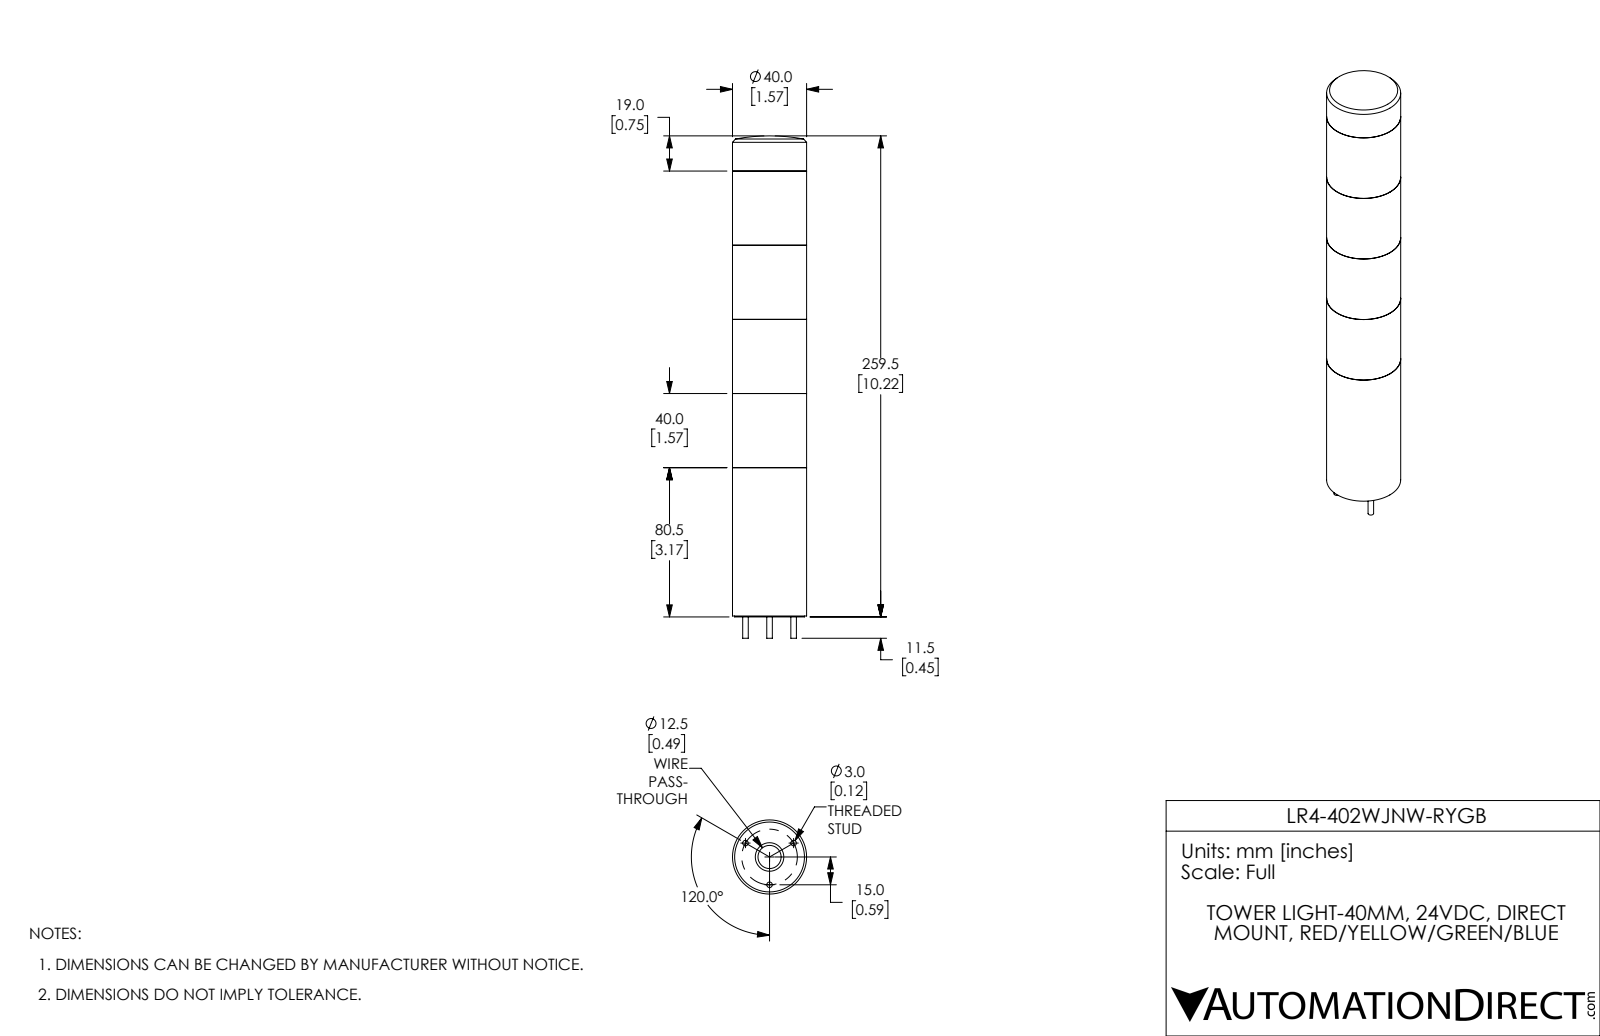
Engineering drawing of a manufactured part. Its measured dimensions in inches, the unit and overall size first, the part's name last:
Units: inches
Overall size (bounding box): 10.669 × 1.575 × 1.575
Round holes (diameter × count): ⌀0.492 ×1, ⌀0.606 ×1, ⌀1.366 ×1, ⌀1.386 ×1, ⌀1.461 ×1, ⌀1.463 ×1
Round bosses / shafts (diameter × count): ⌀0.118 ×3, ⌀1.575 ×1, ⌀1.484 ×1
Main face-to-face distances: 1.575, 3.15, 4.724, 6.299, 0.406, 1.98, 1.169, 3.555, 0.126, 0.28
Volume: 19.78 in³ · Surface area: 92.13 in²
Bodies: 6 solids, 104 faces (37 planar, 64 cylindrical, 3 other)
Part name (STEP PRODUCT): LR4-402WJNW-RYGB
STEP written by: SolidWorks 2017 (AUTOMOTIVE_DESIGN)
